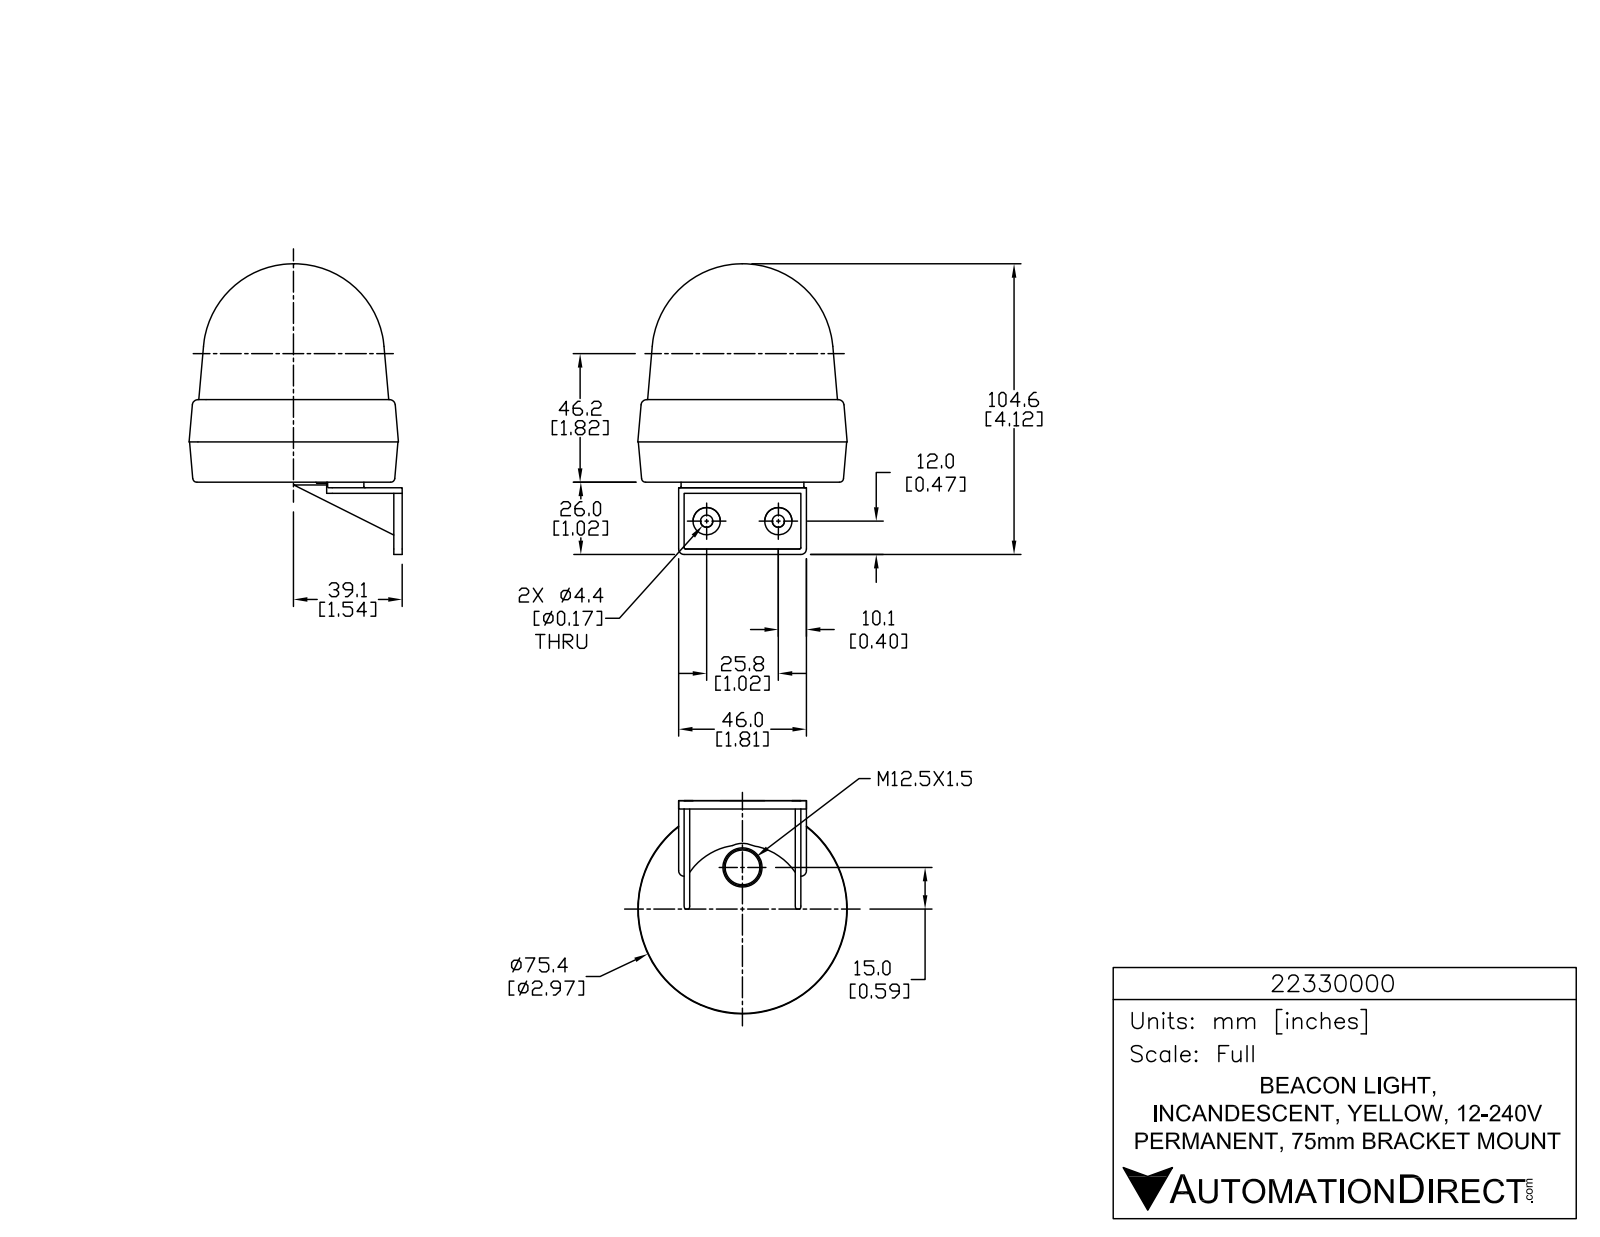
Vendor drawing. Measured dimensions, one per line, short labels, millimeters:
name: 22330000
written by: SolidWorks 2015 (AUTOMOTIVE_DESIGN)
unit: mm
bodies: 1 solid, 819 faces (549 planar, 180 cylindrical, 90 other)
size: 104.6 × 82.6 × 75.4
volume: 262 500 mm³; area: 27 080 mm²
holes: 3× ⌀1.5, 2× ⌀4.4
bosses: 3× ⌀8.6, 3× ⌀2.1, 2× ⌀9.8
rounds: 9× R0.1, 6× R0.1, 6× R0.3, 6× R0.3, 6× R0.3, 6× R0.5, 6× R5, 4× R2
face distances: 2, 4, 40, 1, 3, 42, 38, 2, 42, 44
hole spacings: 25.8
